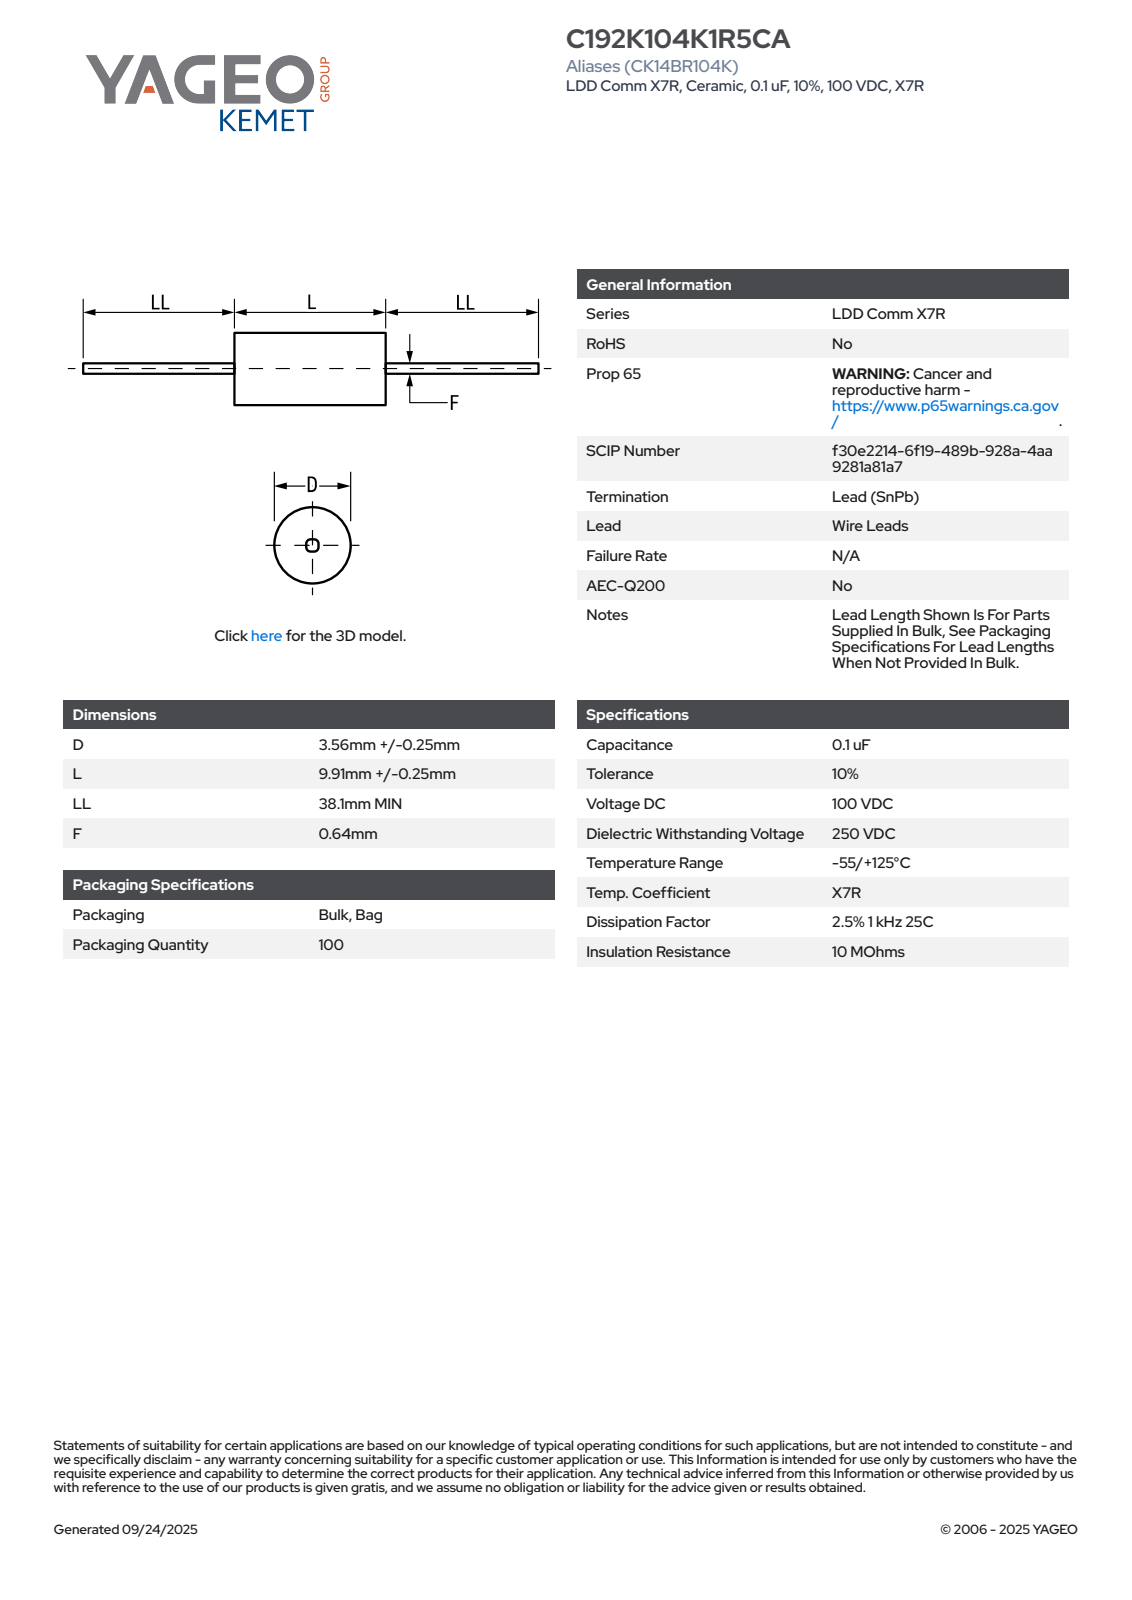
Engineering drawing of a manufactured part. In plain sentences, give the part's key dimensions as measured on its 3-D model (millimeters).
The part is named "CCA_AXM_C192_D3.81L10.16LL38.1F0.64". Its 3-D file was written by "SolidWorks 2014 (AUTOMOTIVE_DESIGN)". It is 1 solid with 66 faces: 26 planar, 9 cylindrical and 31 other. Overall it measures 86.36 by 3.81 by 3.81 millimeters. Its volume is 140 cubic millimeters and its surface area 298 square millimeters. Round bosses or shafts: 1 of diameter 3.81, 1 of diameter 0.64. Partial cylindrical surfaces (rounded edges, fillets, slot ends): 1 of radius 1.9. The main face-to-face distances are 10.16, 38.1, 48.26, 86.36.
